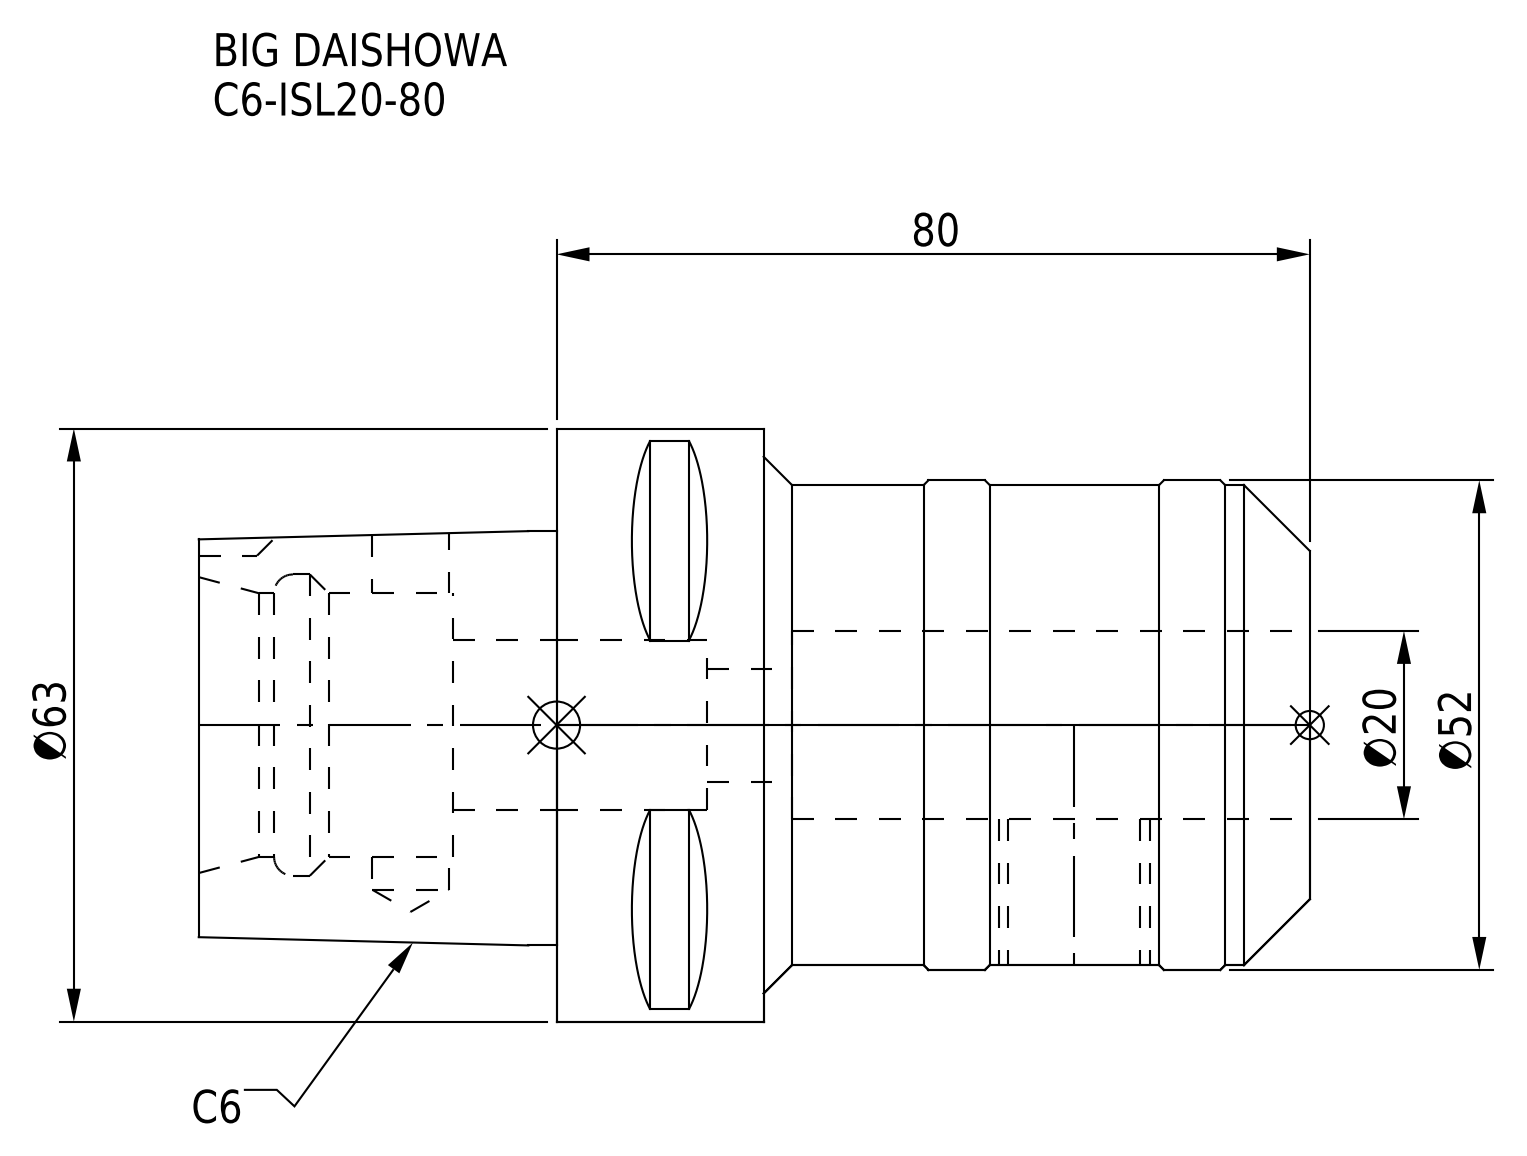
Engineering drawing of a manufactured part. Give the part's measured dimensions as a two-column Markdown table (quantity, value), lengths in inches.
| quantity | value |
| --- | --- |
| part name | C6-ISL20-80 |
| STEP written by | CREO PARAMETRIC BY PTC INC, 2016380 (AUTOMOTIVE_DESIGN) |
| units | inches |
| bodies | 1 solid, 80 faces (29 planar, 29 cylindrical, 22 other) |
| overall size | 4.646 × 2.48 × 2.48 |
| volume | 11.9 in³ |
| surface area | 49.9 in² |
| round holes (diameter × count) | 0.319 × 1, 0.472 × 1, 0.709 × 1, 0.787 × 1, 1.102 × 1, 1.26 × 1 |
| round bosses / shafts (diameter × count) | 2.48 × 1, 2.047 × 1, 2.008 × 1 |
| partial cylindrical surfaces (radius × count) | 0.197 × 1 |
| main face-to-face distances | 3.15, 2.283, 0.866, 1.063, 4.646, 2.362, 1.496, 3.583, 1.299, 0.433 |
